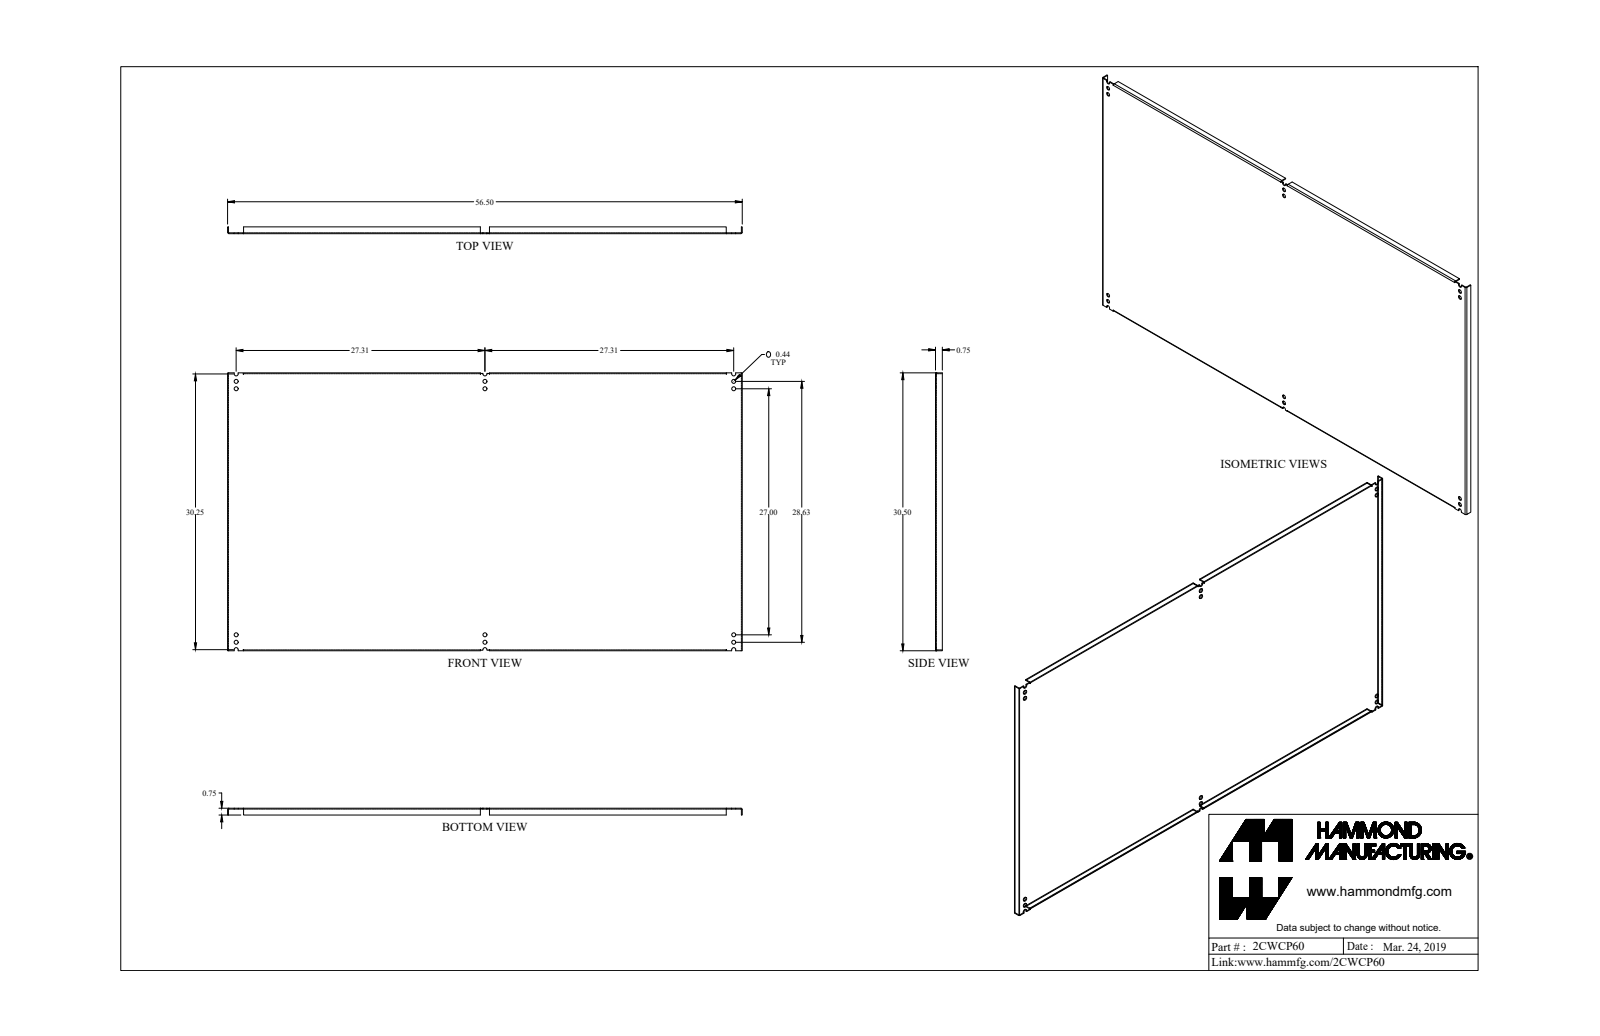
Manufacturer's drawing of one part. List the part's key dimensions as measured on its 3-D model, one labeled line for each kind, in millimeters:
Part name (STEP PRODUCT): 2CWCP60
STEP written by: SolidWorks 2018 (AUTOMOTIVE_DESIGN)
Units: millimetres
Bodies: 3 solids, 111 faces (78 planar, 33 cylindrical, 0 other)
Overall size (bounding box): 1435.1 × 774.6 × 27.2
Volume: 2 838 000 mm³ · Surface area: 2 365 000 mm²
Round holes (diameter × count): ⌀11.1 ×12, ⌀7.8 ×1, ⌀11.3 ×1
Round bosses / shafts (diameter × count): ⌀25.4 ×1
Partial cylindrical surfaces — rounded edges, fillets, slot ends (radius × count): R1.2 ×4, R3.6 ×4, R5.6 ×4, R5.6 ×2
Main face-to-face distances: 2.4, 772.2, 1432.7, 774.6, 769.8, 1435.1, 1430.3, 19.1, 16.6, 2.4
Hole centre spacings: 693.8, 694.1, 990.1, 975.5, 1005, 1387.5, 1387.7, 20.6
